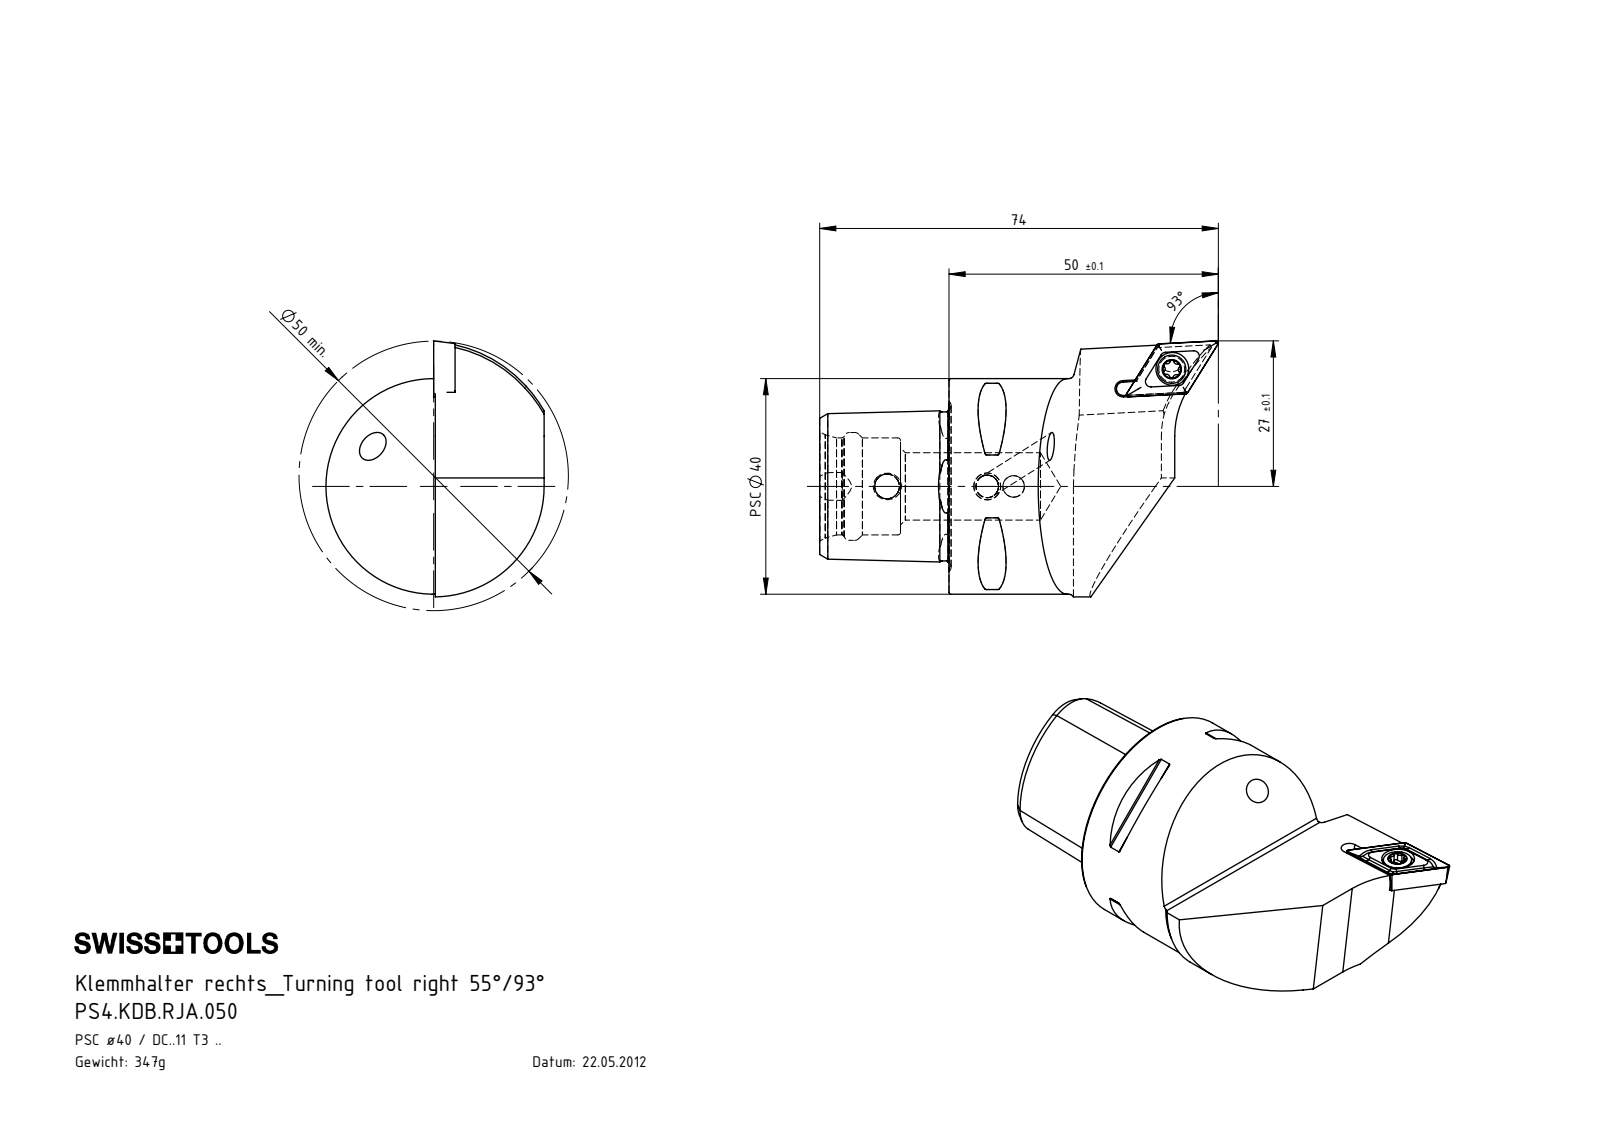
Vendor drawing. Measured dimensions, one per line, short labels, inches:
name: PS4-KDB.RJA.050; WCB-ER2.001.009_A; KVT_MB_600_050; DCMT11T304 (+1 more)
written by: SolidWorks 2012 (CONFIG_CONTROL_DESIGN)
unit: in
bodies: 5 solids, 283 faces (51 planar, 70 cylindrical, 162 other)
size: 2.914 × 1.87 × 1.594
volume: 2.695 in³; area: 19.46 in²
holes: 2× ⌀0.157, 2× ⌀0.165, 1× ⌀0.13, 1× ⌀0.173, 1× ⌀0.181, 1× ⌀0.197, 1× ⌀0.24, 1× ⌀0.492, 1× ⌀0.709, 1× ⌀0.787
bosses: 1× ⌀1.575, 1× ⌀0.207, 1× ⌀0.197, 1× ⌀0.157
rounds: 8× R0.012, 6× R0.013, 6× R0.023, 1× R0.031, 1× R0.049, 1× R0.118, 1× R0.669, 1× R0.807
face distances: 0.795, 0.945, 0.651, 0.144, 0.611, 1.39, 0.354, 0.591, 0.937, 0.346
hole spacings: 0.925, 1.438, 1.443, 2.25, 2.255
